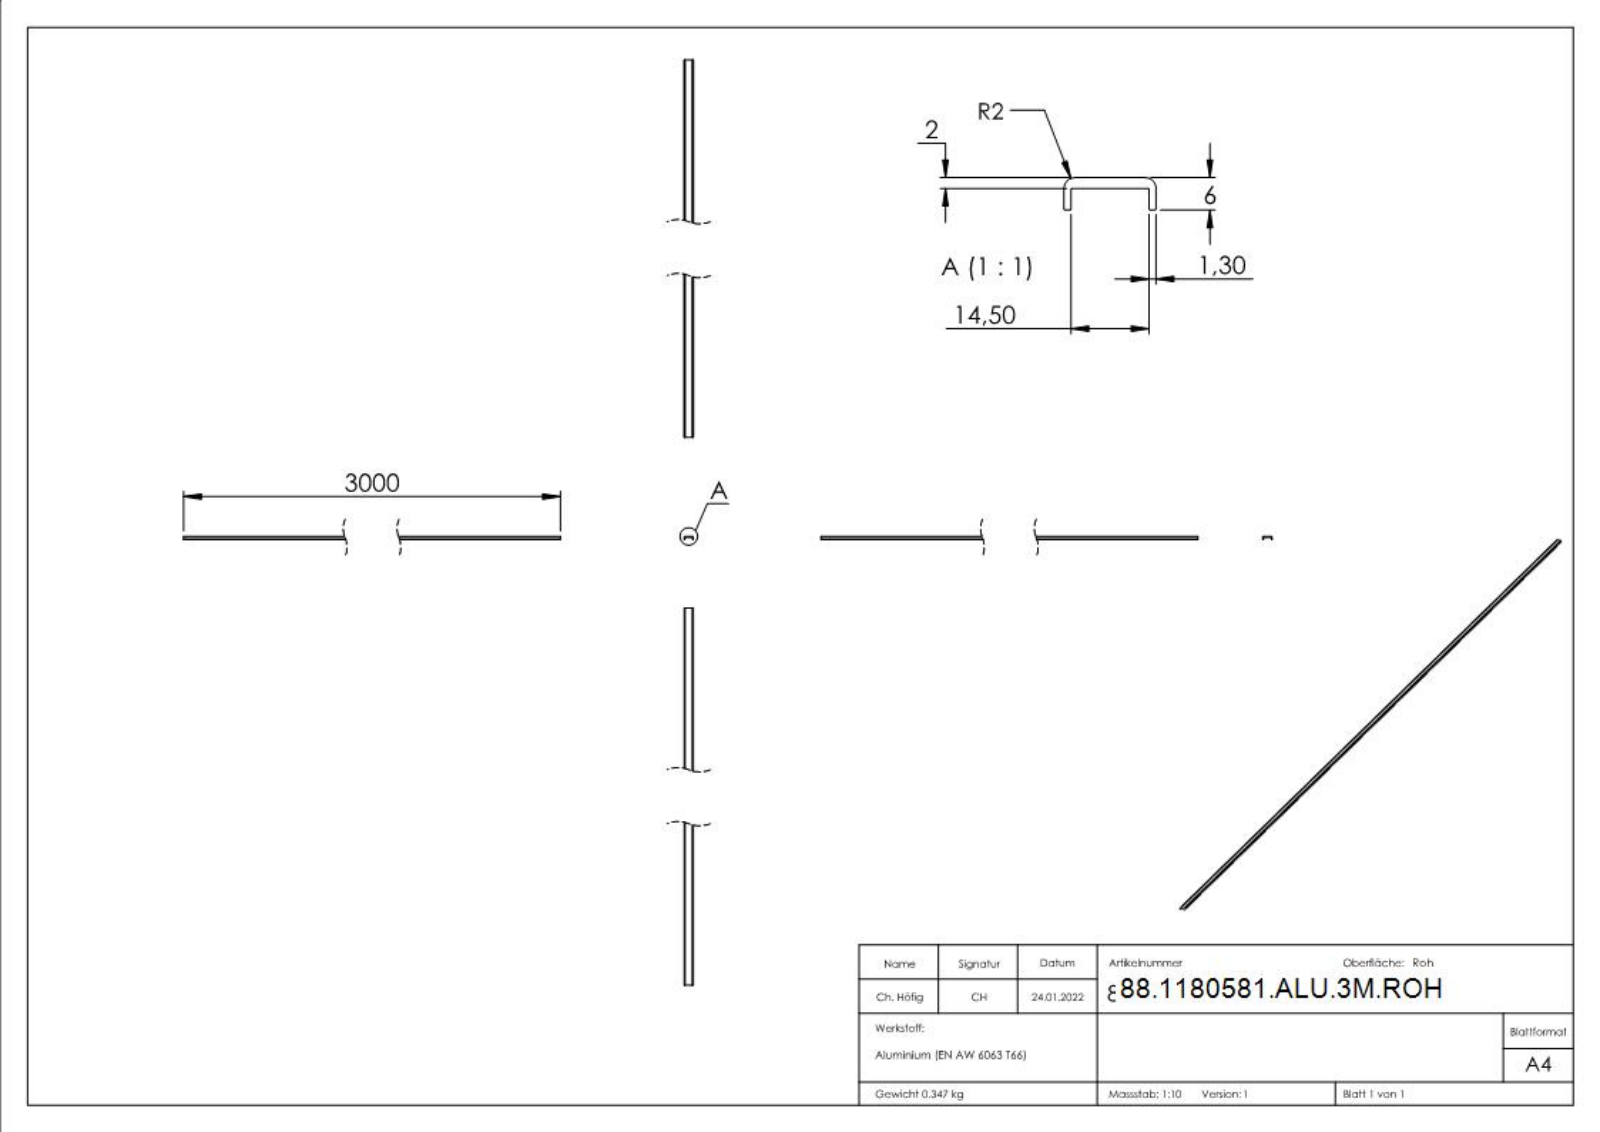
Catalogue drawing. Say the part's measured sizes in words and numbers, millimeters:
The part is named "80581-ALU-3M-ROH". Its 3-D file was written by "SolidWorks 2018 (CONFIG_CONTROL_DESIGN)". It is 1 solid with 342 faces: 195 planar, 8 cylindrical and 139 other. Overall it measures 3000 by 17.1 by 6 millimeters. Its volume is 128 598 cubic millimeters and its surface area 156 000 square millimeters. Partial cylindrical surfaces (rounded edges, fillets, slot ends): 6 of radius 0.2, 2 of radius 2. The main face-to-face distances are 2, 1.3, 15.8, 17.1, 14.5, 6, 4, 3000, 4.1, 1.9.
